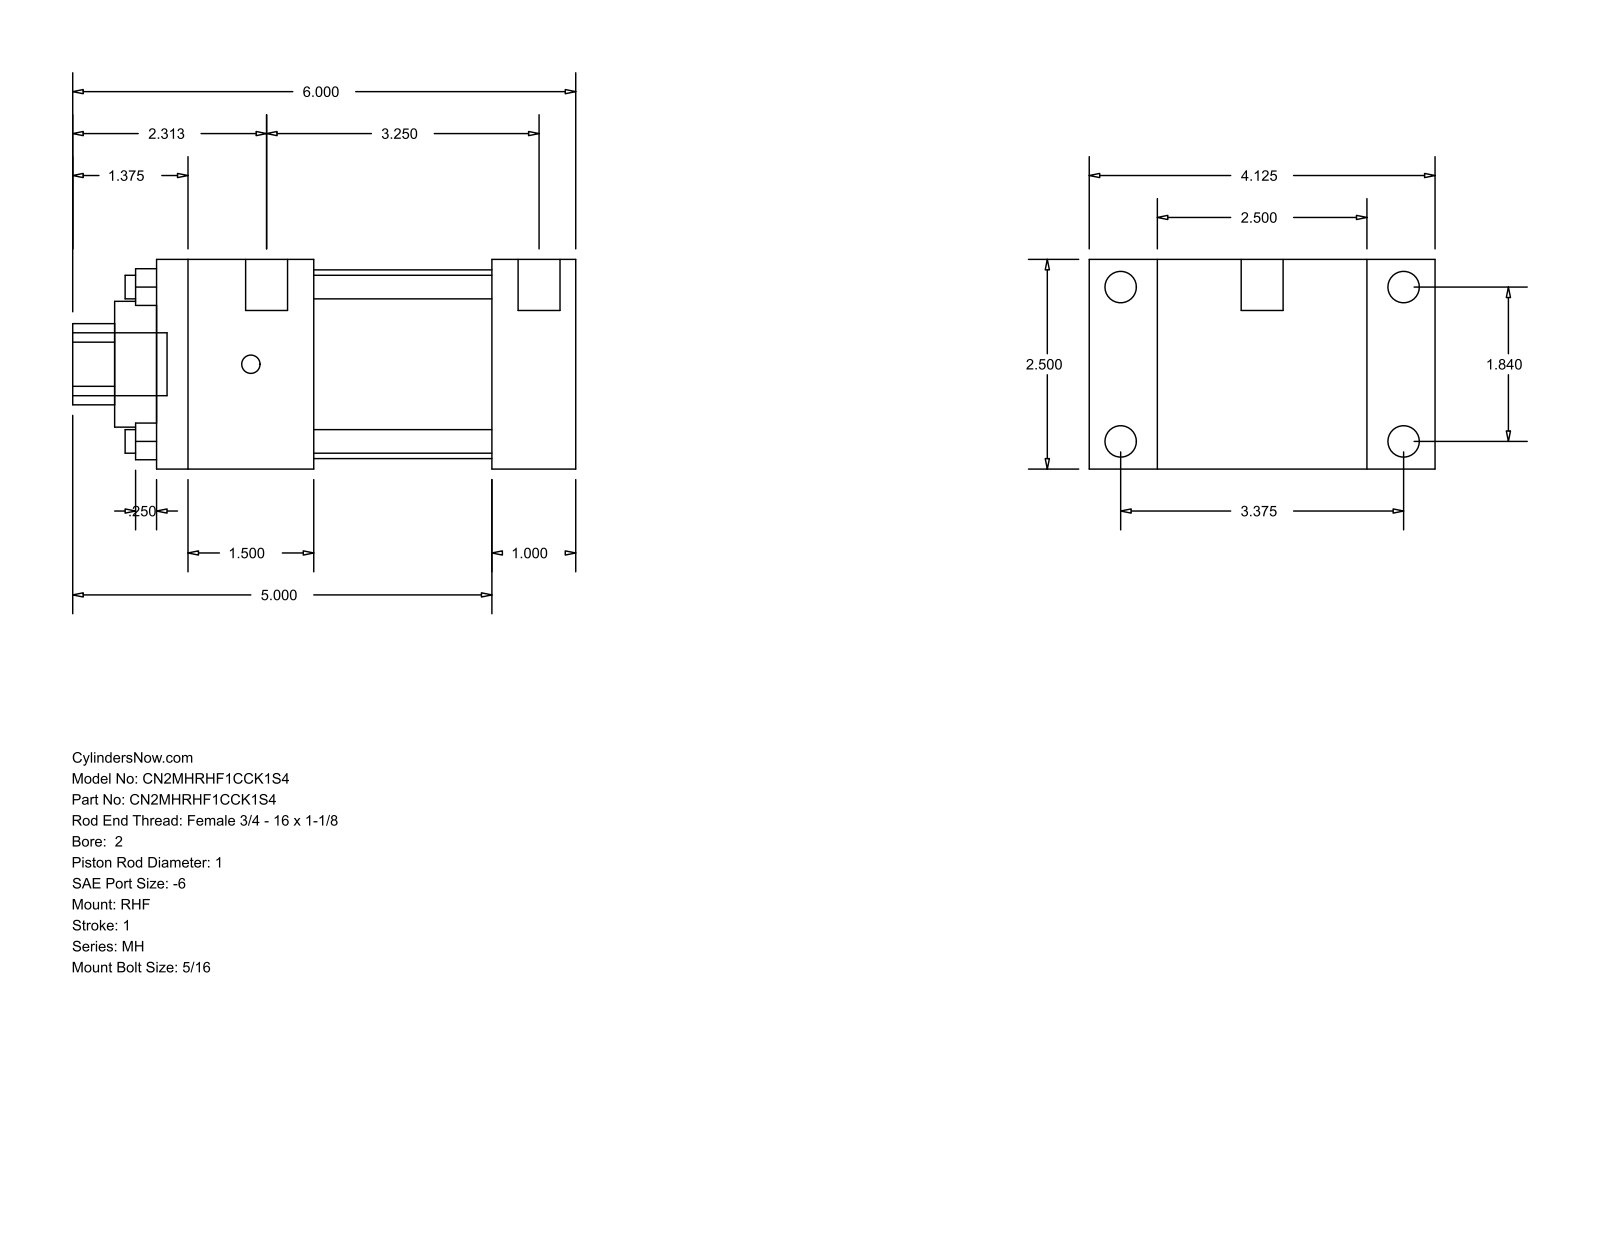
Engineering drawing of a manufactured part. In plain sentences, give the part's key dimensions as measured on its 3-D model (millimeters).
The part is named "MH_RHF__0200_1". Its 3-D file was written by "GSSL Pune (CONFIG_CONTROL_DESIGN)". It is 0 solids with 88 faces: 60 planar, 28 cylindrical and 0 other. Overall it measures 152.4 by 104.78 by 63.5 millimeters. Round holes: 4 of diameter 7.14, 1 of diameter 25.4, 1 of diameter 38.1, 1 of diameter 57.15. Round bosses or shafts: 4 of diameter 9.53, 4 of diameter 5.56, 2 of diameter 12.7, 1 of diameter 19.05. Partial cylindrical surfaces (rounded edges, fillets, slot ends): 1 of radius 12.29. The main face-to-face distances are 63.5, 25.4, 20.64, 84.14, 127, 101.6, 104.78, 47.63, 53.97, 79.37. The hole center spacings are 33.05, 46.74, 66.1.
